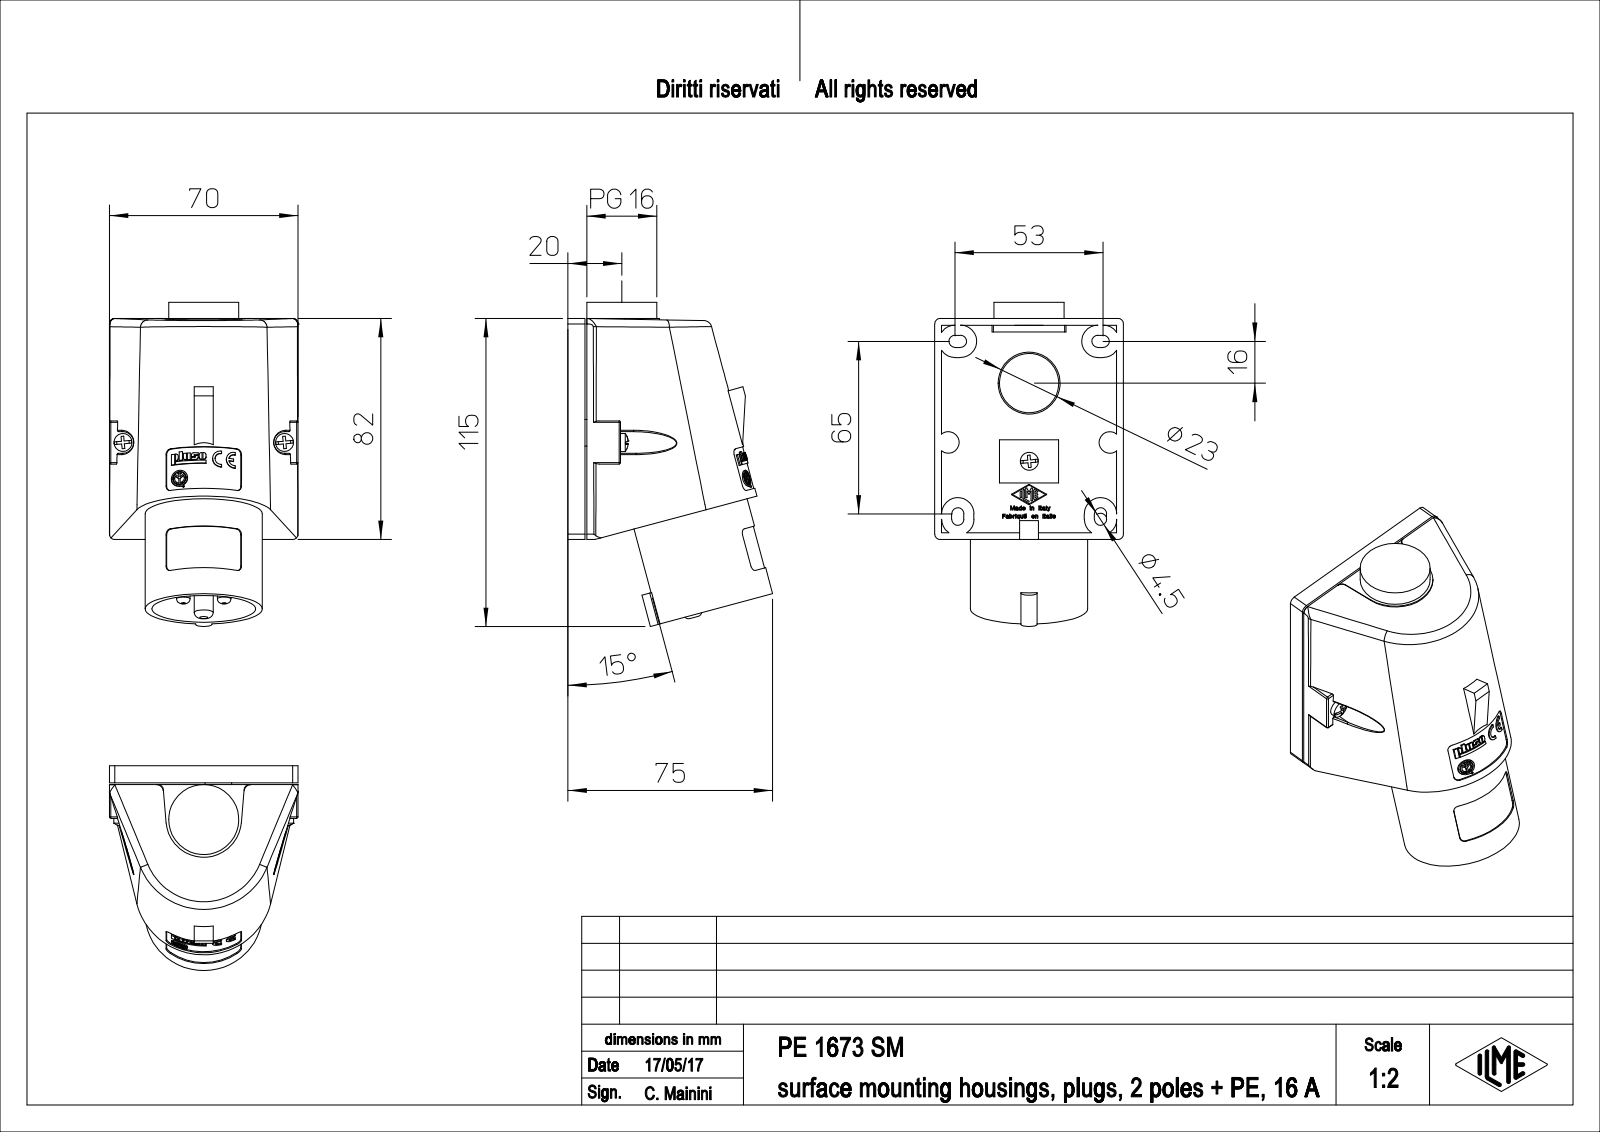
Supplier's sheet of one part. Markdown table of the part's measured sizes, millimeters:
| quantity | value |
| --- | --- |
| part name | PE_1673_SM |
| STEP written by | PTC Creo Elements/Direct Modeling 19.0E 27-Jun-2016 (C) Parametric Technology GmbH (AUTOMOTIVE_DESIGN) |
| units | millimeters |
| bodies | 1 solid, 1394 faces (1127 planar, 167 cylindrical, 100 other) |
| overall size | 120.27 × 75.98 × 70 |
| volume | 248 744 mm³ |
| surface area | 55 760 mm² |
| round holes (diameter × count) | 3.2 × 2, 4.5 × 2, 4.2 × 1, 5.04 × 1, 21.3 × 1, 23 × 1, 24 × 1, 38.5 × 1 |
| round bosses / shafts (diameter × count) | 6.7 × 5, 5 × 2, 43.5 × 1, 37 × 1, 26 × 1, 7 × 1, 6 × 1 |
| partial cylindrical surfaces (radius × count) | 2 × 16, 0.25 × 15, 0.5 × 9, 0.85 × 9, 2.25 × 8, 4 × 8, 6 × 8, 0.12 × 3 |
| main face-to-face distances | 0.65, 6, 5.35, 7, 1, 6.35, 70, 2.5, 3, 82 |
| hole center spacings | 30.81, 37.2, 29, 60 |
